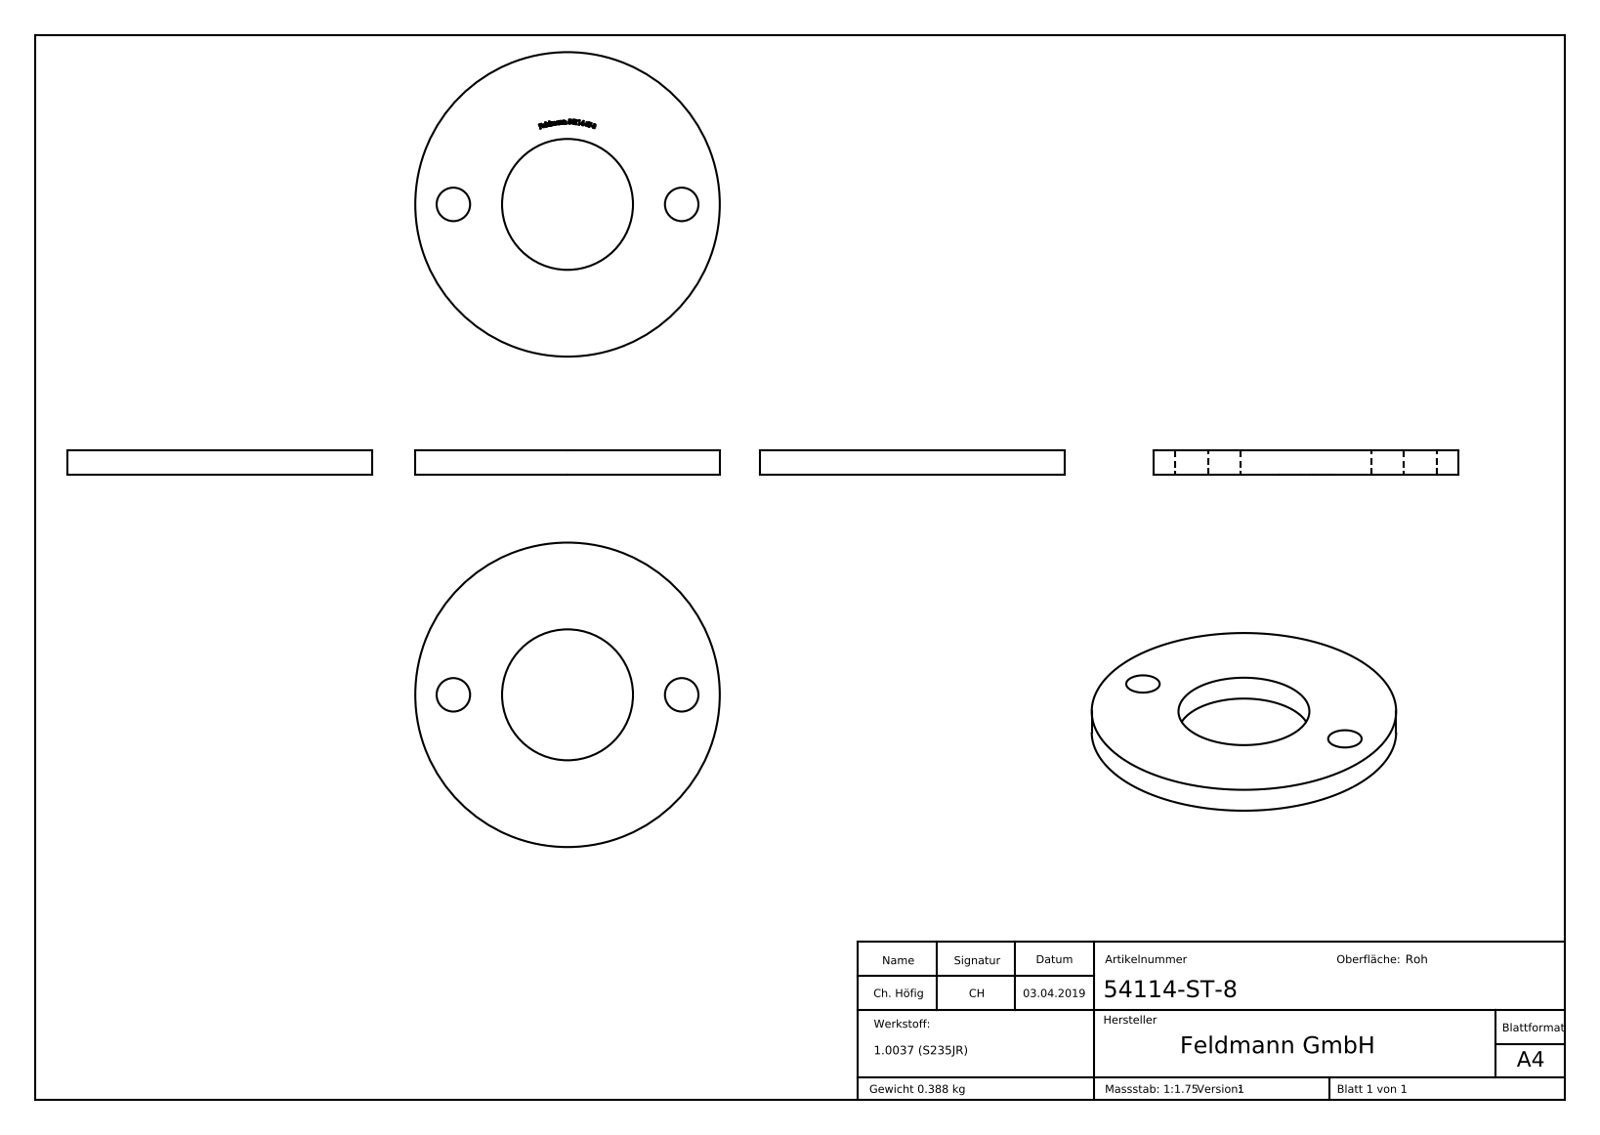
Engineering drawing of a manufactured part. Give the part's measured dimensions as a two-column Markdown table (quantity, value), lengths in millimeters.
| quantity | value |
| --- | --- |
| part name | 54114-ST-8 |
| STEP written by | SolidWorks 2015 (CONFIG_CONTROL_DESIGN) |
| units | millimeters |
| bodies | 1 solid, 239 faces (143 planar, 8 cylindrical, 88 other) |
| overall size | 100 × 100 × 8 |
| volume | 49 693 mm³ |
| surface area | 16 579 mm² |
| round holes (diameter × count) | 11 × 2, 43 × 1 |
| round bosses / shafts (diameter × count) | 100 × 1 |
| main face-to-face distances | 8, 7.9, 0.54, 0.85, 0.72, 0.73, 0.66, 0.6, 0.67, 0.41 |
| hole center spacings | 37.5, 75 |
